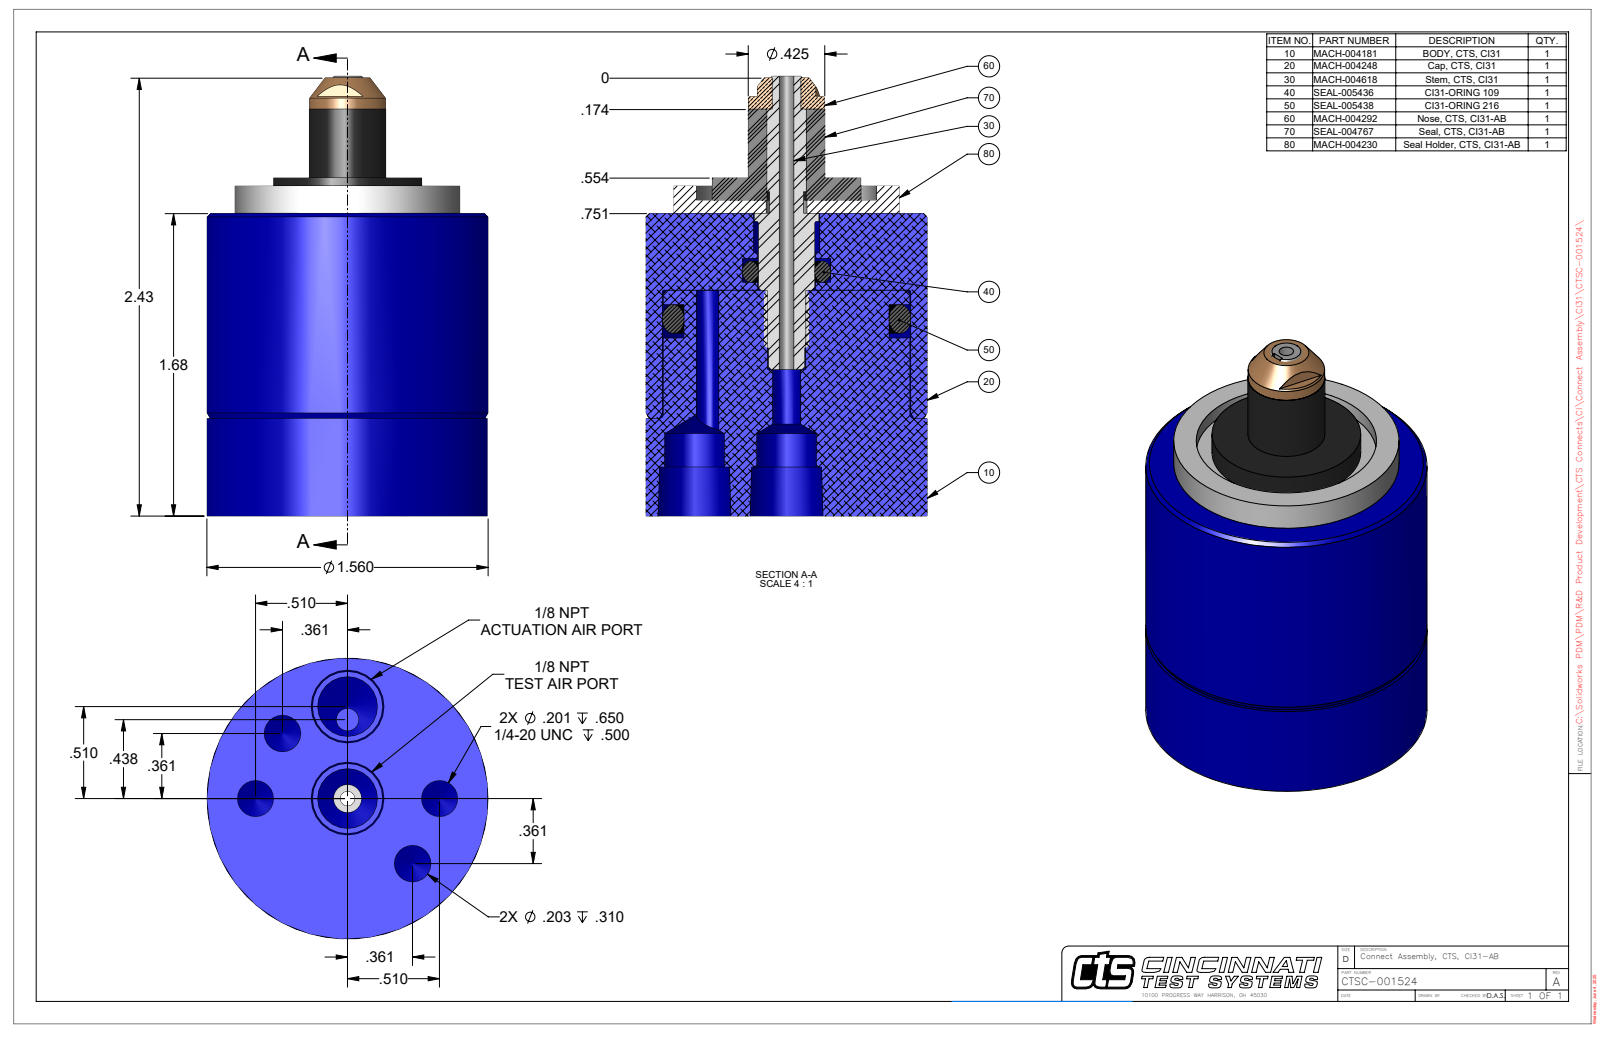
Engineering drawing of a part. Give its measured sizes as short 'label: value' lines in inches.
name: CTSC-001524
written by: SolidWorks 2023 (AUTOMOTIVE_DESIGN)
unit: in
bodies: 1 solid, 95 faces (25 planar, 42 cylindrical, 28 other)
size: 2.437 × 1.56 × 1.56
volume: 3.272 in³; area: 19.39 in²
holes: 2× ⌀0.201, 2× ⌀0.203, 2× ⌀0.332, 1× ⌀0.081, 1× ⌀0.125, 1× ⌀0.156, 1× ⌀0.368, 1× ⌀1, 1× ⌀1.377
bosses: 1× ⌀1.56, 1× ⌀1.365, 1× ⌀1.25, 1× ⌀0.825, 1× ⌀0.427, 1× ⌀0.424, 1× ⌀0.357
rounds: 1× R0.079
face distances: 1.677, 1.829, 0.152, 1.874, 0.197, 0.045, 1.749, 0.072, 0.08, 0.125
hole spacings: 0.51, 0.39, 0.942, 0.672, 0.721, 0.072, 0.369, 0.437
